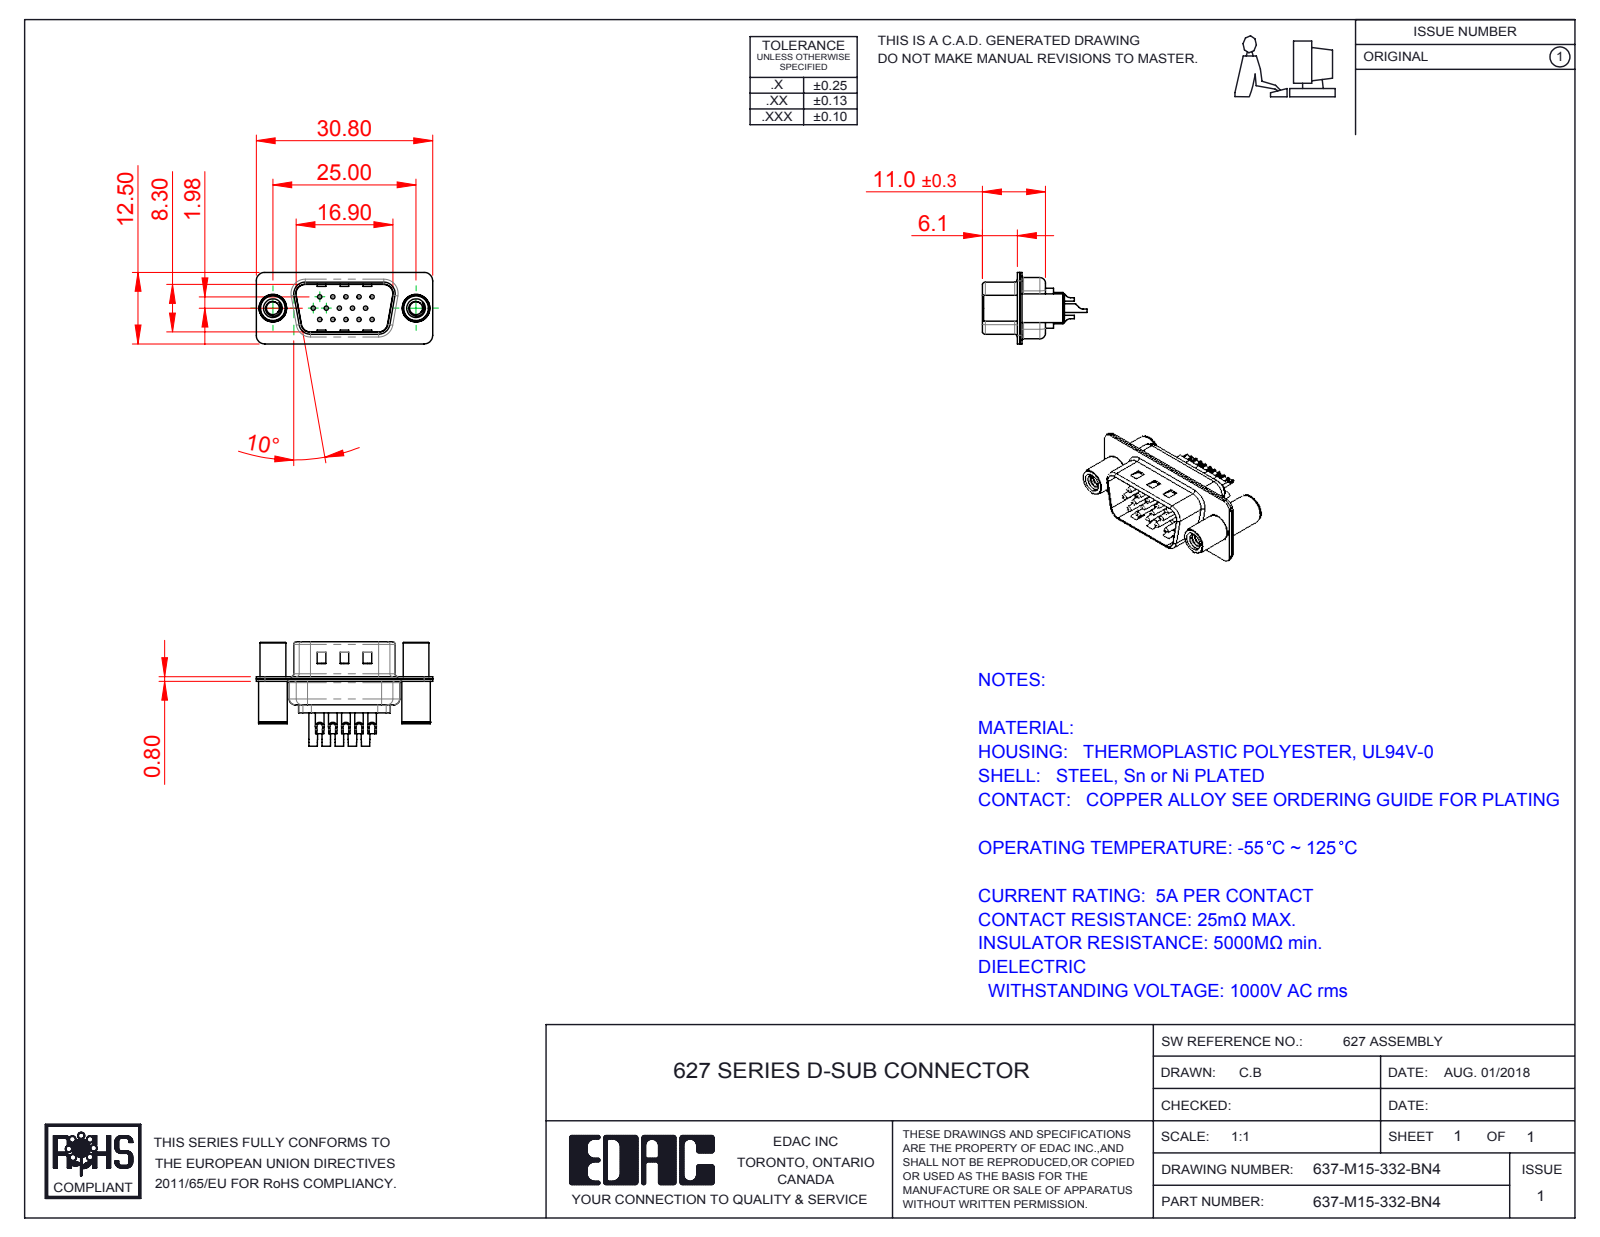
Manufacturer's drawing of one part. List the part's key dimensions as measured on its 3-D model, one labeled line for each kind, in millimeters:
Part name (STEP PRODUCT): 637M Contact Row 2_32; 637M Contact Row 1_32; 637-M15-332-BN4; 637M 4-40 Threaded Standoff and Board Spacer (+4 more)
STEP written by: SolidWorks 2016 (CONFIG_CONTROL_DESIGN)
Units: millimetres
Bodies: 20 solids, 945 faces (248 planar, 421 cylindrical, 276 other)
Overall size (bounding box): 30.8 × 18.25 × 12.5
Volume: 1 685 mm³ · Surface area: 4 805 mm²
Round holes (diameter × count): ⌀0.75 ×15, ⌀1 ×15, ⌀1.6 ×15, ⌀2 ×15, ⌀2.26 ×2, ⌀3.26 ×2, ⌀4 ×2, ⌀4.8 ×2
Round bosses / shafts (diameter × count): ⌀1.5 ×15, ⌀5 ×2, ⌀4.9 ×2, ⌀4.5 ×2
Partial cylindrical surfaces — rounded edges, fillets, slot ends (radius × count): R1.5 ×16, R2 ×12, R0.5 ×8, R1.6 ×8, R1 ×7, R0.25 ×4, R0.6 ×4, R0.65 ×4
Main face-to-face distances: 0.4, 0.8, 9.5, 9.1, 0.65, 8.7, 9.9, 0.75, 0.35, 1.2
Hole centre spacings: 3.96, 2.28, 2.29, 4.57, 6.05, 6.86, 7.92, 6.04
